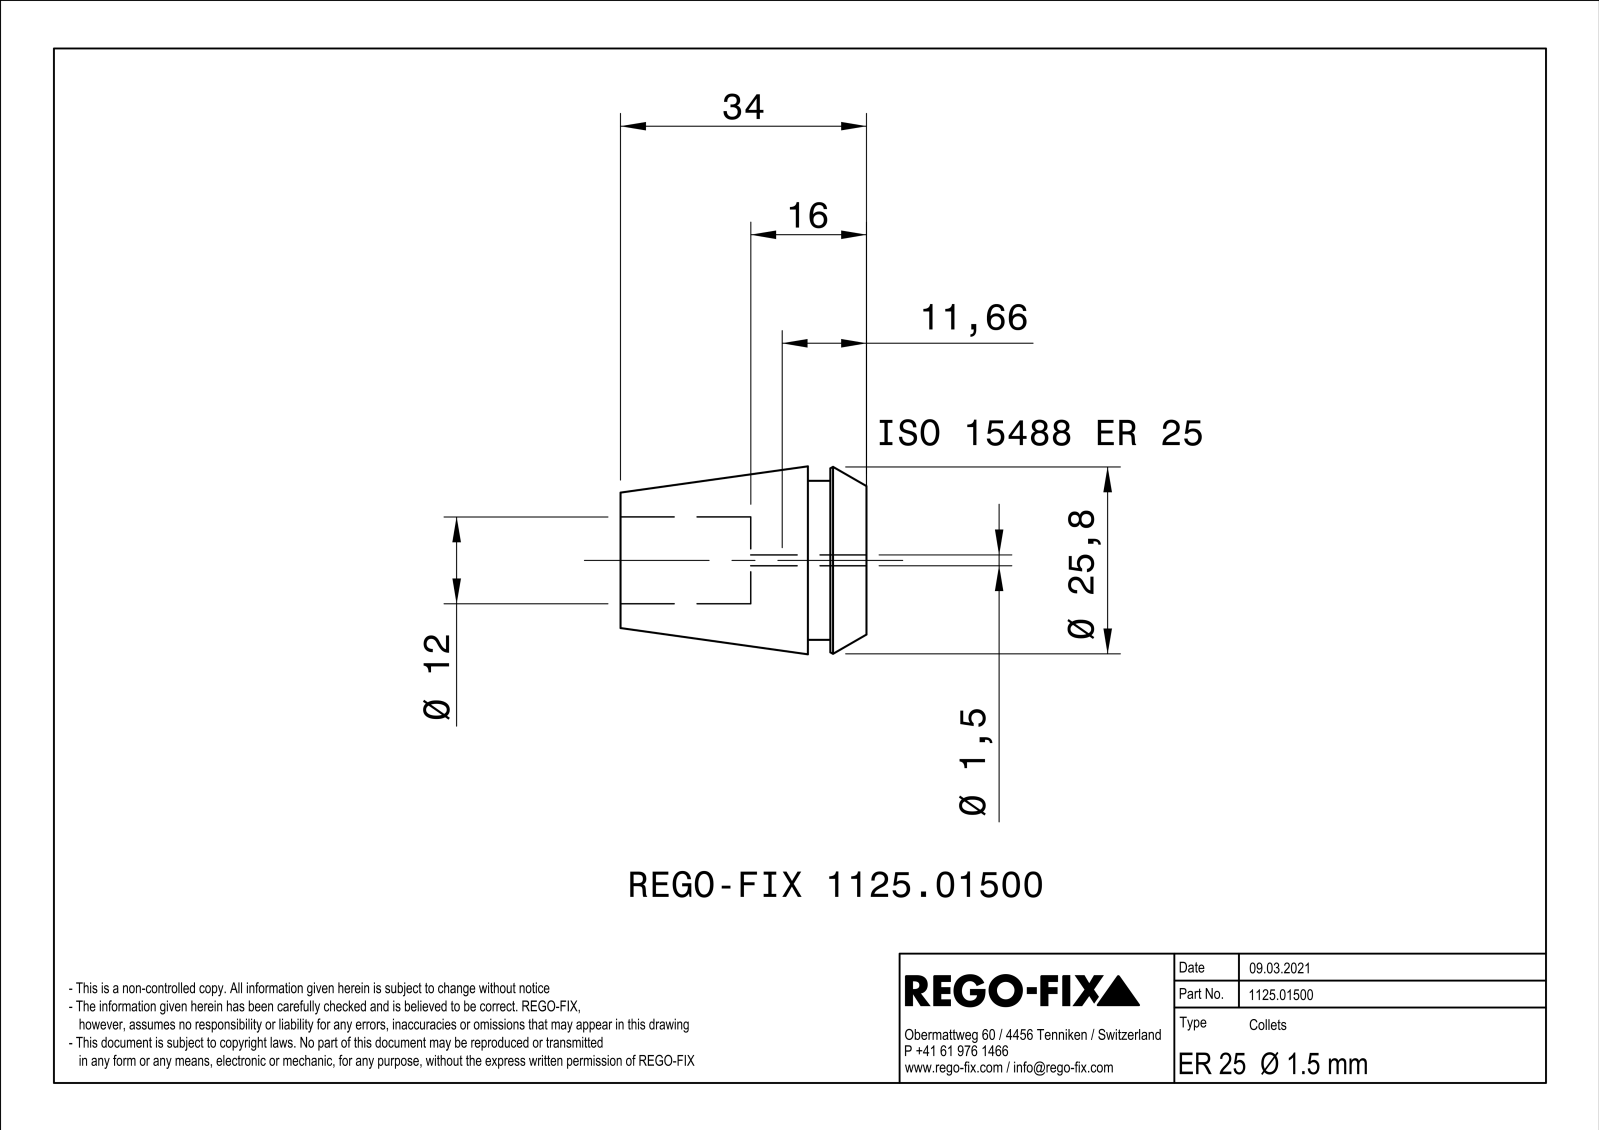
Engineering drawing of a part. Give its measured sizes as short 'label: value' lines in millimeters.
name: NOCUT
written by: SIEMENS PLM Software Solid Edge ST10 (AUTOMOTIVE_DESIGN)
unit: mm
bodies: 1 solid, 268 faces (100 planar, 56 cylindrical, 112 other)
size: 34 × 25.99 × 25.99
volume: 9 204 mm³; area: 9 338 mm²
holes: 1× ⌀12
bosses: 1× ⌀22
rounds: 14× R0.4, 8× R40, 1× R0.75
face distances: 0.8, 0.78, 0.82, 8.1, 34, 25.9, 0.63, 5, 3.1, 29
